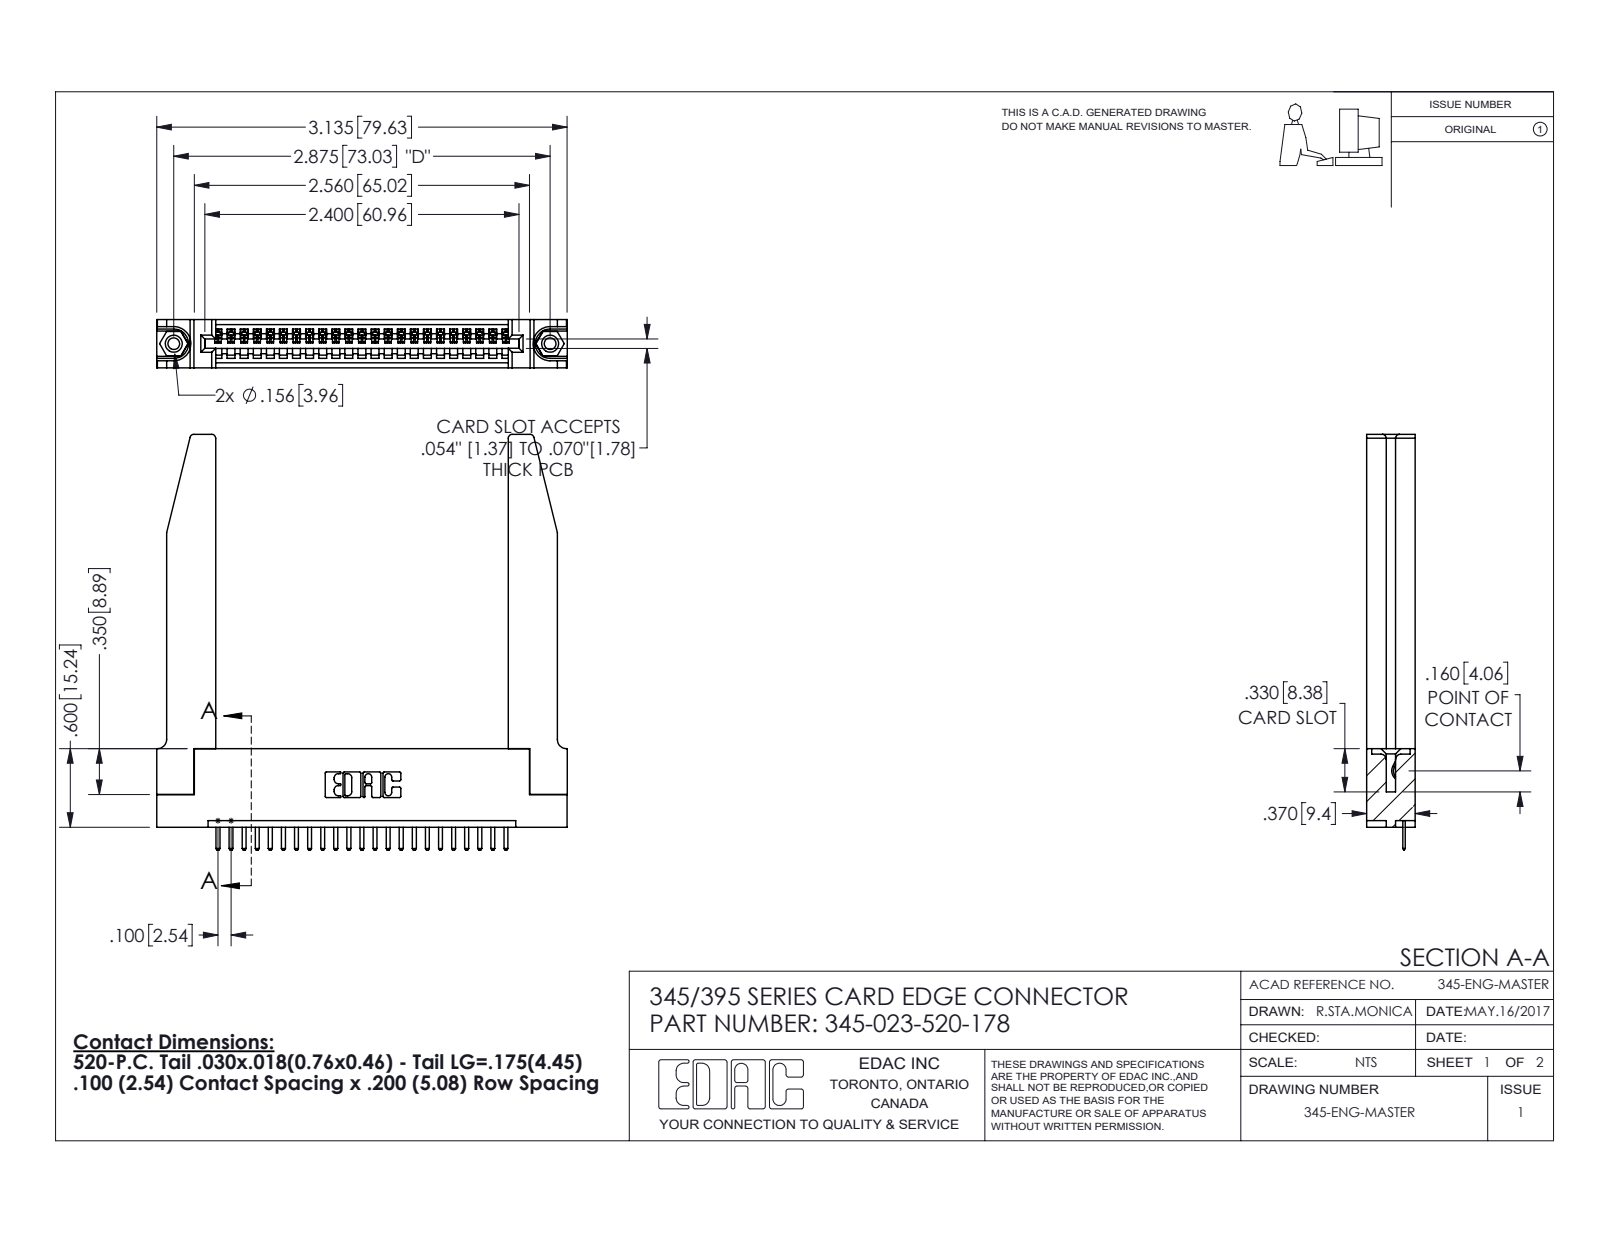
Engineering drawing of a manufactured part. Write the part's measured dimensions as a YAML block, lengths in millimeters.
part_name: "345-220-078_345-220-078; 345-023-520-178; 345-250-001_345-250-001-102; 345 Part_Flush Mounting Lugs - 0.156 Dia-TH (+1 more)"
step_written_by: "SolidWorks 2016 (CONFIG_CONTROL_DESIGN)"
units: millimeters
bodies: {solids: 28, faces: 1786, planar: 1188, cylindrical: 546, other: 52}
overall_size: [80.6, 79.7, 9.4]
volume: 15100
surface_area: 16130
round_holes:
  - {diameter: 2.3, count: 2}
  - {diameter: 3.2, count: 2}
  - {diameter: 4, count: 2}
  - {diameter: 1.6, count: 1}
round_bosses_or_shafts:
  - {diameter: 3.9, count: 2}
partial_cylinders:
  - {radius: 0.3, count: 48}
  - {radius: 0.2, count: 46}
  - {radius: 0.3, count: 22}
  - {radius: 0.8, count: 8}
  - {radius: 0.2, count: 6}
  - {radius: 0.8, count: 6}
  - {radius: 0.7, count: 3}
  - {radius: 0.8, count: 2}
face_to_face_distances: [9.4, 1.8, 7.6, 5.1, 3.8, 3.8, 2.5, 6.9, 0.6, 2]
hole_center_spacings: [6.9, 67.1, 73]
